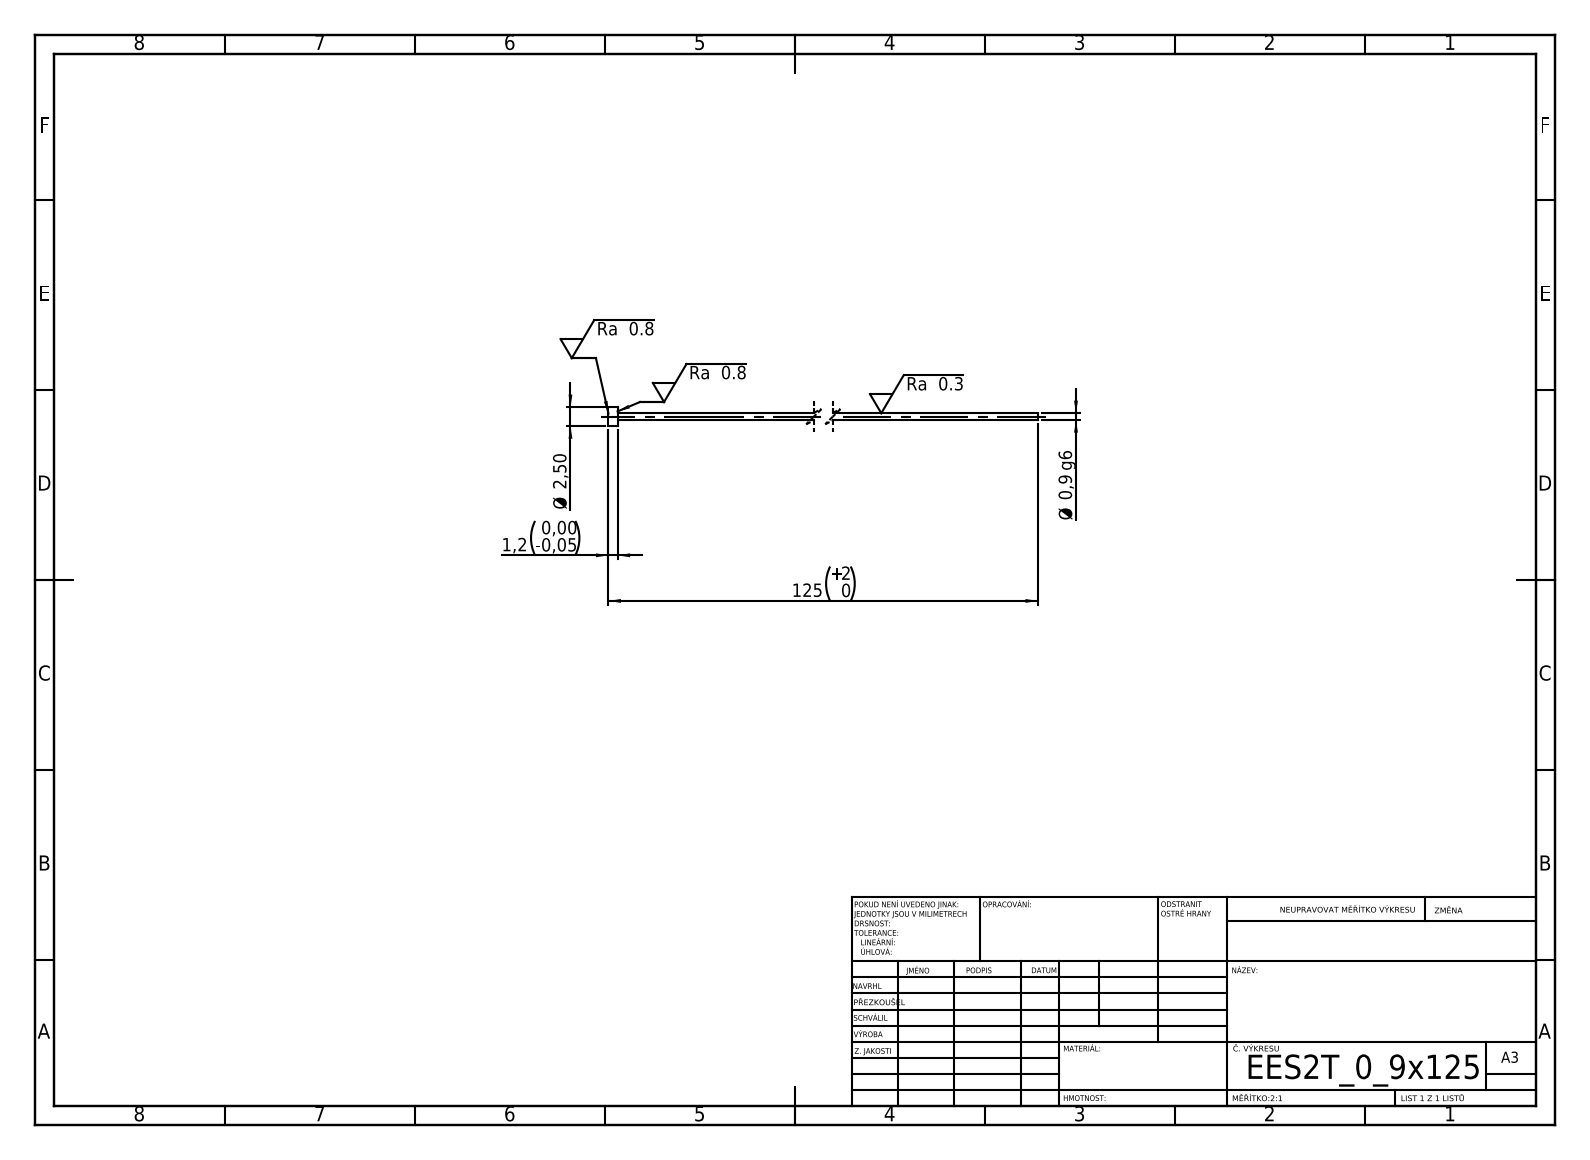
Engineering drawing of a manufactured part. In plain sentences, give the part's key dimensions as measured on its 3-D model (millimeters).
Its 3-D file was written by "SolidWorks 2019 (CONFIG_CONTROL_DESIGN)". It is 1 solid with 7 faces: 3 planar, 4 cylindrical and 0 other. Overall it measures 125 by 2.5 by 2.5 millimeters. Its volume is 85 cubic millimeters and its surface area 369 square millimeters. Round bosses or shafts: 1 of diameter 2.5, 1 of diameter 0.9. The main face-to-face distances are 1.2, 125, 123.8.
